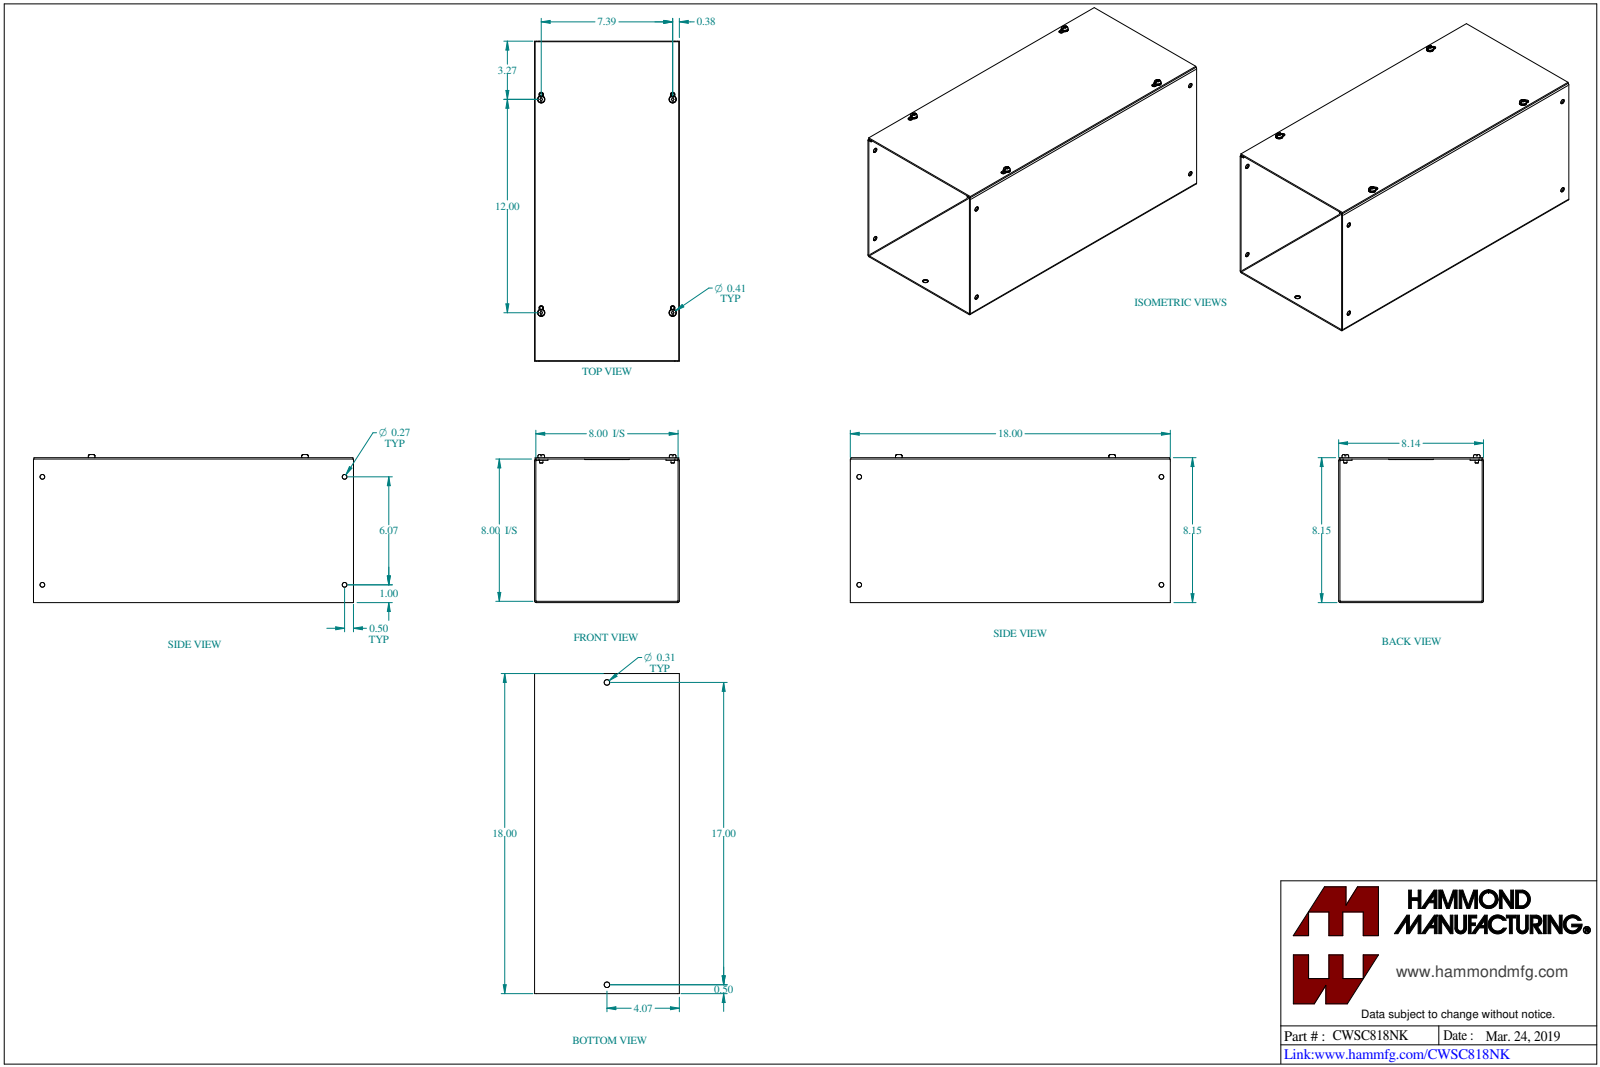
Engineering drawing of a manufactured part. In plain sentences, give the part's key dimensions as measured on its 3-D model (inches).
The part is named "CWSC818NK". Its 3-D file was written by "SolidWorks 2023 (CONFIG_CONTROL_DESIGN)". It is 6 solids with 180 faces: 88 planar, 68 cylindrical and 24 other. Overall it measures 18 by 8.325 by 8.144 inches. Its volume is 44.04 cubic inches and its surface area 1 211 square inches. Round holes: 4 of diameter 0.177, 4 of diameter 0.266, 2 of diameter 0.313. Round bosses or shafts: 4 of diameter 0.375, 4 of diameter 0.19. Partial cylindrical surfaces (rounded edges, fillets, slot ends): 4 of radius 0.036, 4 of radius 0.108, 4 of radius 0.125, 4 of radius 0.203. The main face-to-face distances are 0.072, 8.072, 8, 0.078, 8.15, 8.078, 8.144, 7.928, 0.15, 0.031. The hole center spacings are 4.463, 14.964, 17, 6.072, 7.394, 12, 14.095, 18.052.
